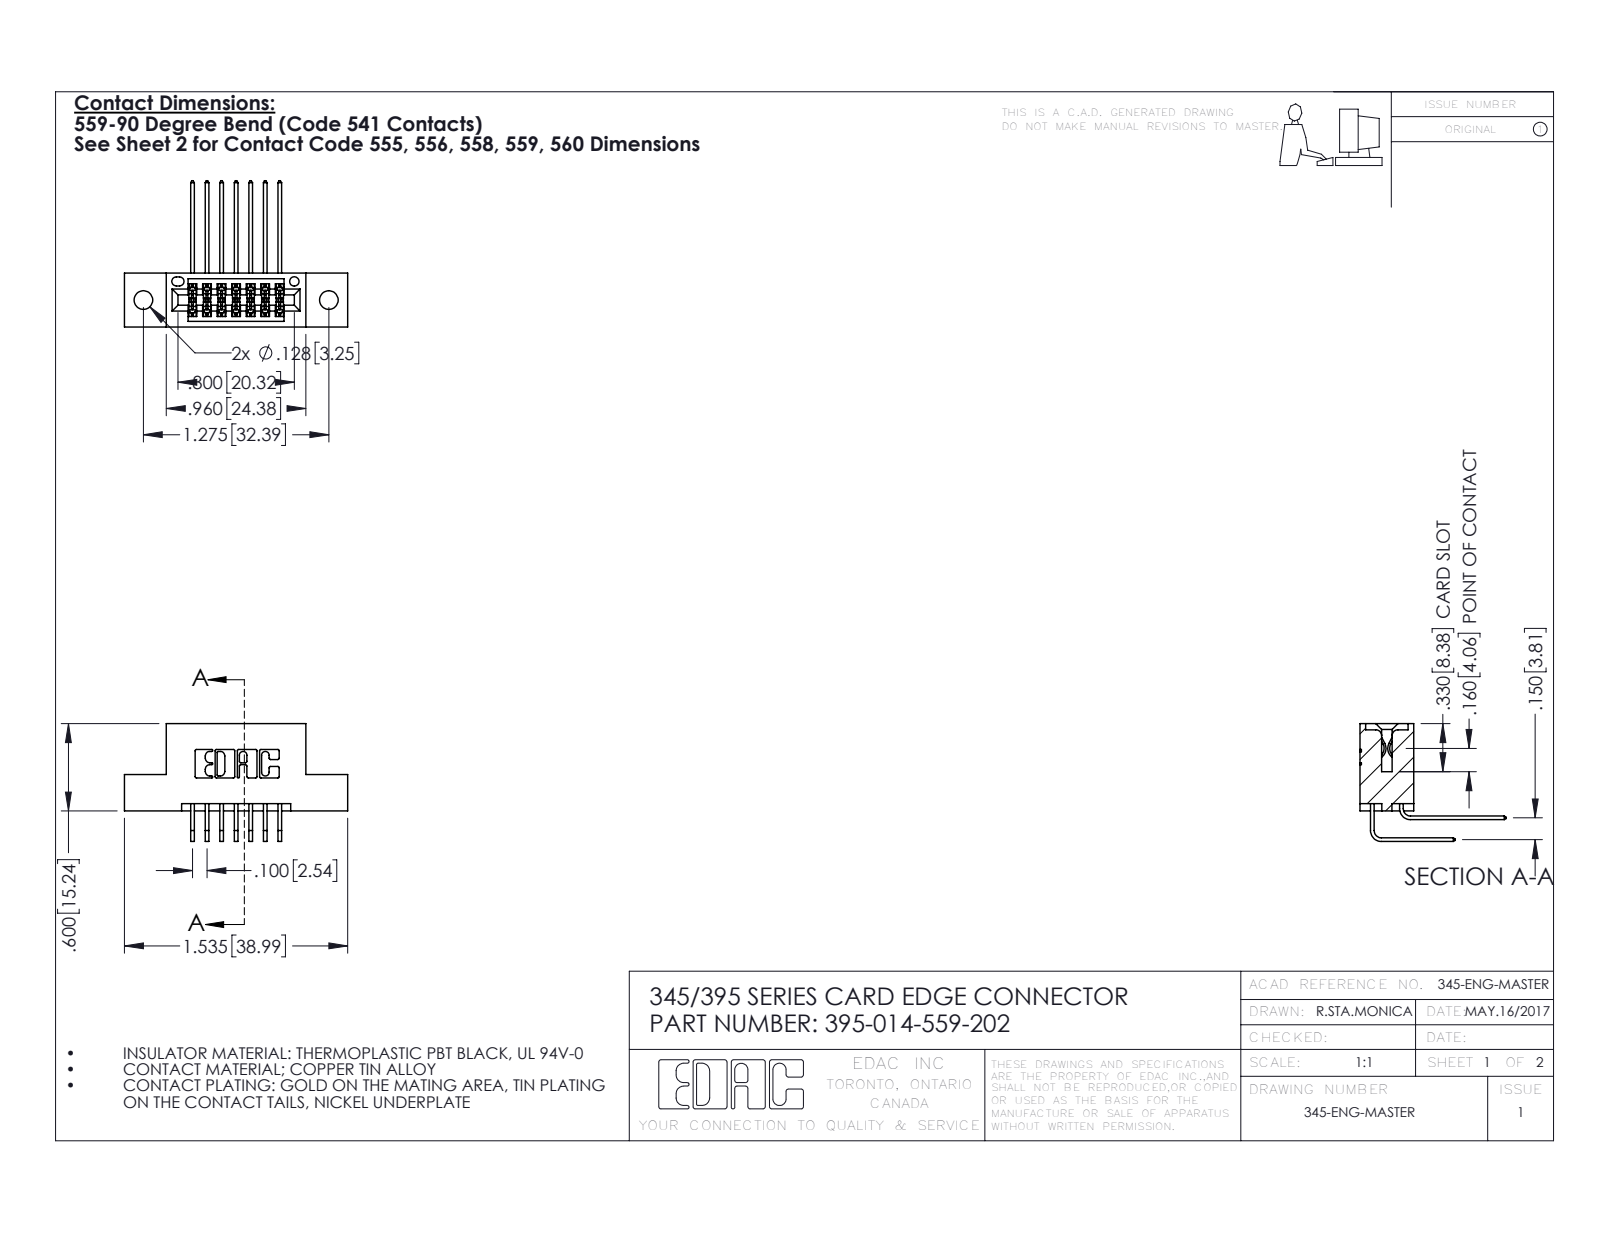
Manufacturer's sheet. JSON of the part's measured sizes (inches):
{"part_name": "345-292-001_558 559 Tail - 1; 395-014-559-202; 345 Part_Flush Mounting Lugs - 0.128 Dia; 345-292-001_559 Tail - 2", "step_written_by": "SolidWorks 2016 (CONFIG_CONTROL_DESIGN)", "units": "inches", "bodies": {"solids": 15, "faces": 854, "planar": 570, "cylindrical": 284, "other": 0}, "overall_size": [1.535, 1.005, 0.809], "volume_in3": 0.214, "surface_area_in2": 7.149, "round_holes": [[0.128, 2], [0.064, 1]], "partial_cylinders_radius": [[0.006, 22], [0.01, 22], [0.007, 6], [0.031, 6], [0.026, 3], [0.014, 2], [0.019, 2], [0.022, 2]], "face_to_face_distances": [0.2, 0.072, 0.298, 0.37, 0.1, 0.098, 0.272, 0.025, 0.3, 0.15], "hole_center_spacings": [0.27, 1.045, 1.275]}
